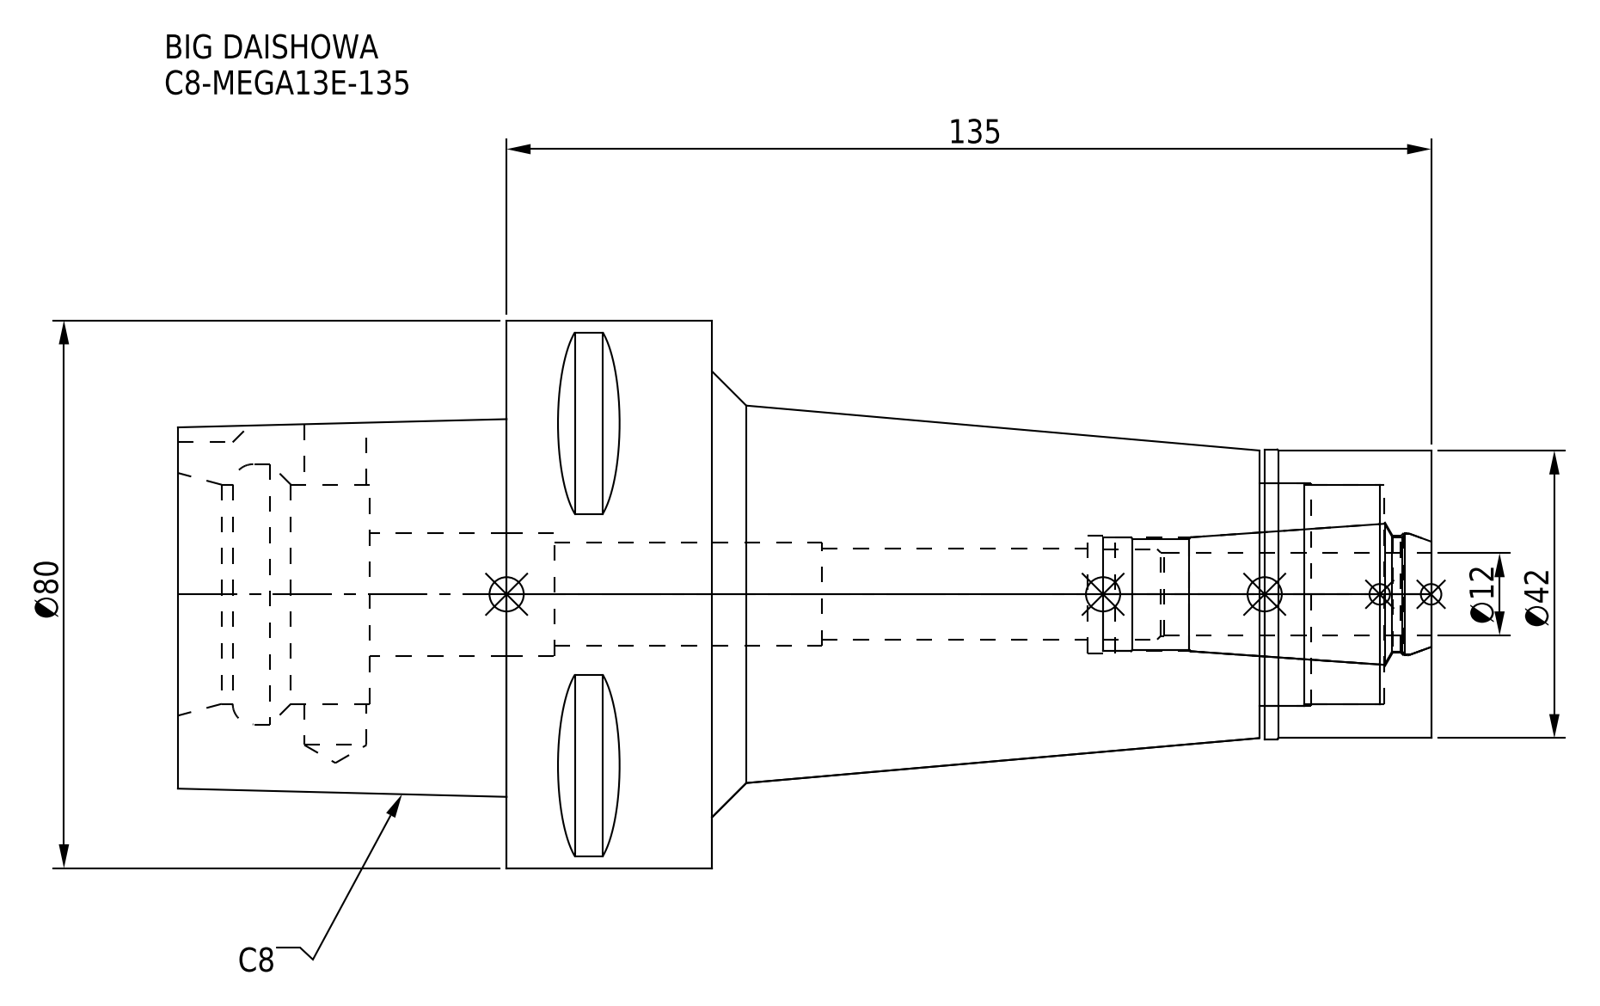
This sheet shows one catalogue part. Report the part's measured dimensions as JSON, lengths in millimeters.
{"part_name": "C8-MEGA13E-135-120-FreeParts; C8-MEGA13E-135; DXF_TEMP_ASSY_ASM_4_ASM.stp; C8-MEGA13E-135_1.stp (+3 more)", "step_written_by": "SolidWorks 2019 (CONFIG_CONTROL_DESIGN)", "units": "millimeters", "bodies": {"solids": 2, "faces": 100, "planar": 37, "cylindrical": 39, "other": 24}, "overall_size": [183, 80, 80], "volume_mm3": 385965, "surface_area_mm2": 56882, "round_holes": [[9.1, 1], [13.3, 1], [15, 1], [16.6, 1], [17, 1], [17.2, 1], [17.9, 1], [18, 1], [32, 1], [32.5, 1], [38, 1]], "round_bosses_or_shafts": [[80, 1], [42.3, 1], [42, 1]], "partial_cylinders_radius": [[6, 1]], "face_to_face_distances": [30, 105, 135, 183, 78, 48, 25.1, 24.3, 80.7, 110.7]}
